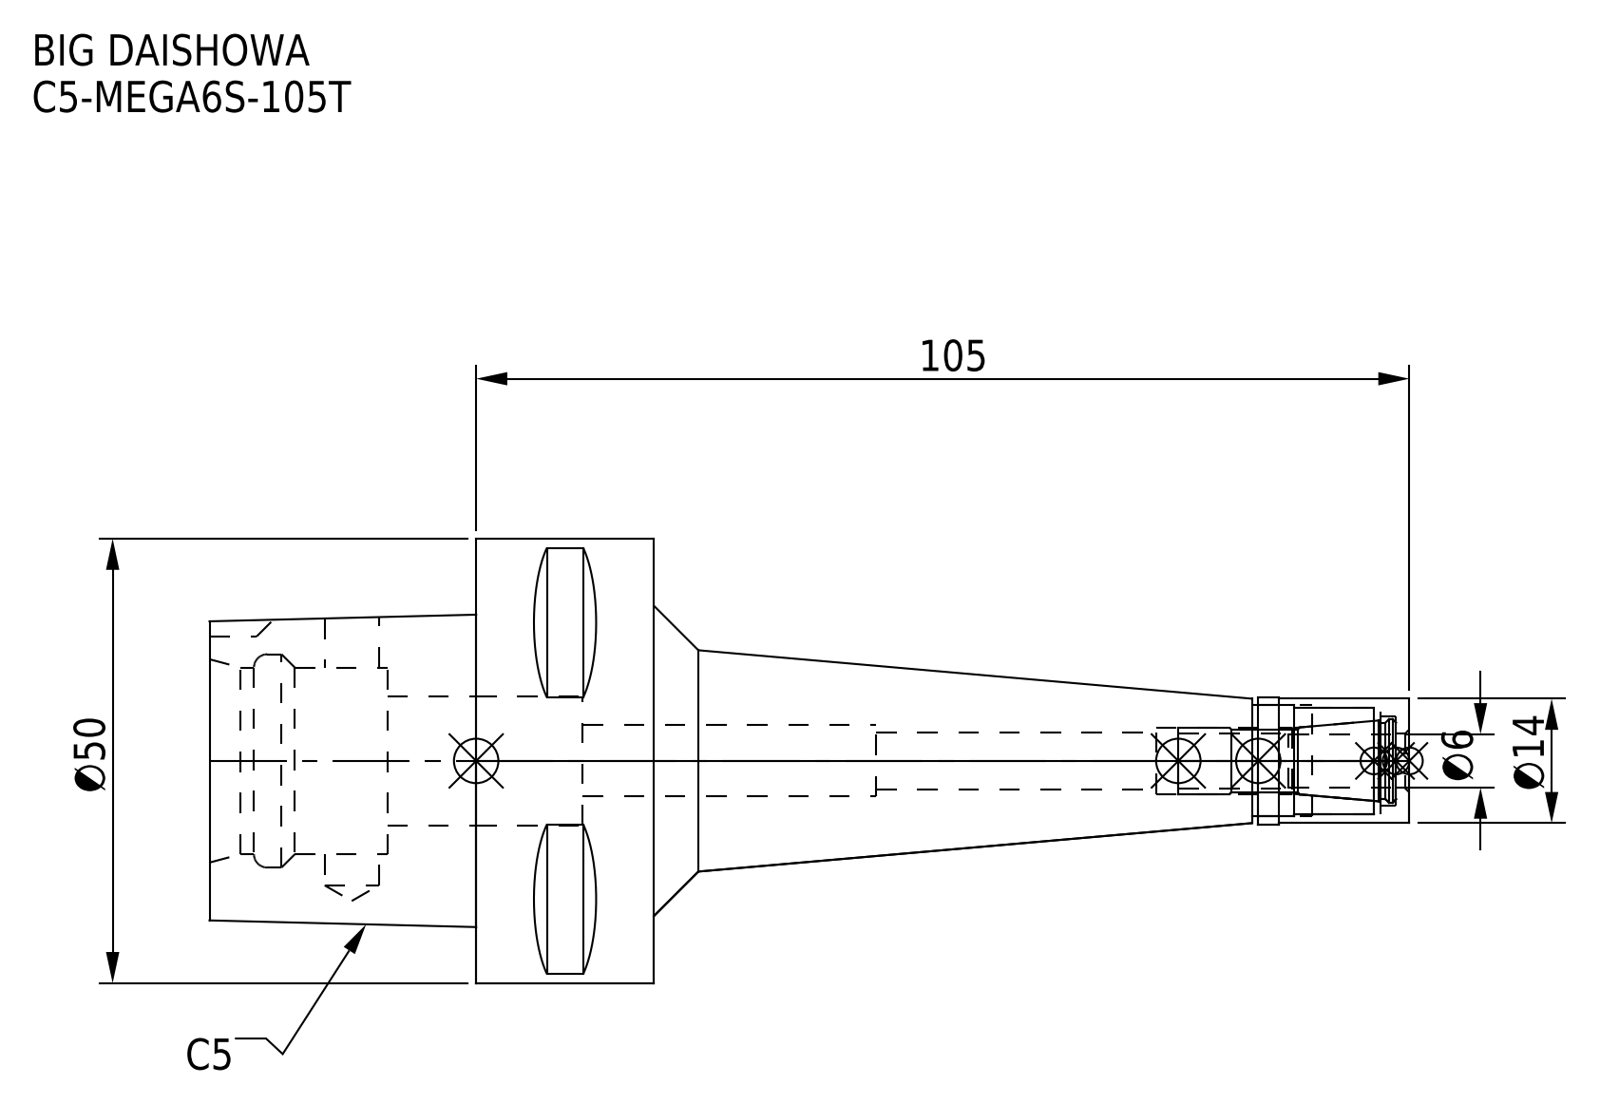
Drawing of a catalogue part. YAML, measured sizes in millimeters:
part_name: "C5-MEGA6S-105T; C5-MEGA6S-105T-060_ASM.stp; DXF_TEMP_ASSY_ASM_4_ASM.stp; MGN6S_1.stp (+3 more)"
step_written_by: "SolidWorks 2019 (CONFIG_CONTROL_DESIGN)"
units: millimeters
bodies: {solids: 2, faces: 93, planar: 38, cylindrical: 37, other: 18}
overall_size: [135, 50, 50]
volume: 75648
surface_area: 20768
round_holes:
  - {diameter: 6.1, count: 2}
  - {diameter: 6.4, count: 1}
  - {diameter: 7.4, count: 1}
  - {diameter: 8, count: 1}
  - {diameter: 10, count: 1}
  - {diameter: 12, count: 1}
  - {diameter: 12.5, count: 1}
  - {diameter: 14.5, count: 1}
  - {diameter: 21, count: 1}
  - {diameter: 24, count: 1}
round_bosses_or_shafts:
  - {diameter: 50, count: 1}
  - {diameter: 14.3, count: 1}
  - {diameter: 14, count: 1}
partial_cylinders:
  - {radius: 4, count: 1}
face_to_face_distances: [20, 30, 50, 44, 10, 19.18, 7.95, 12.05, 115, 8]
